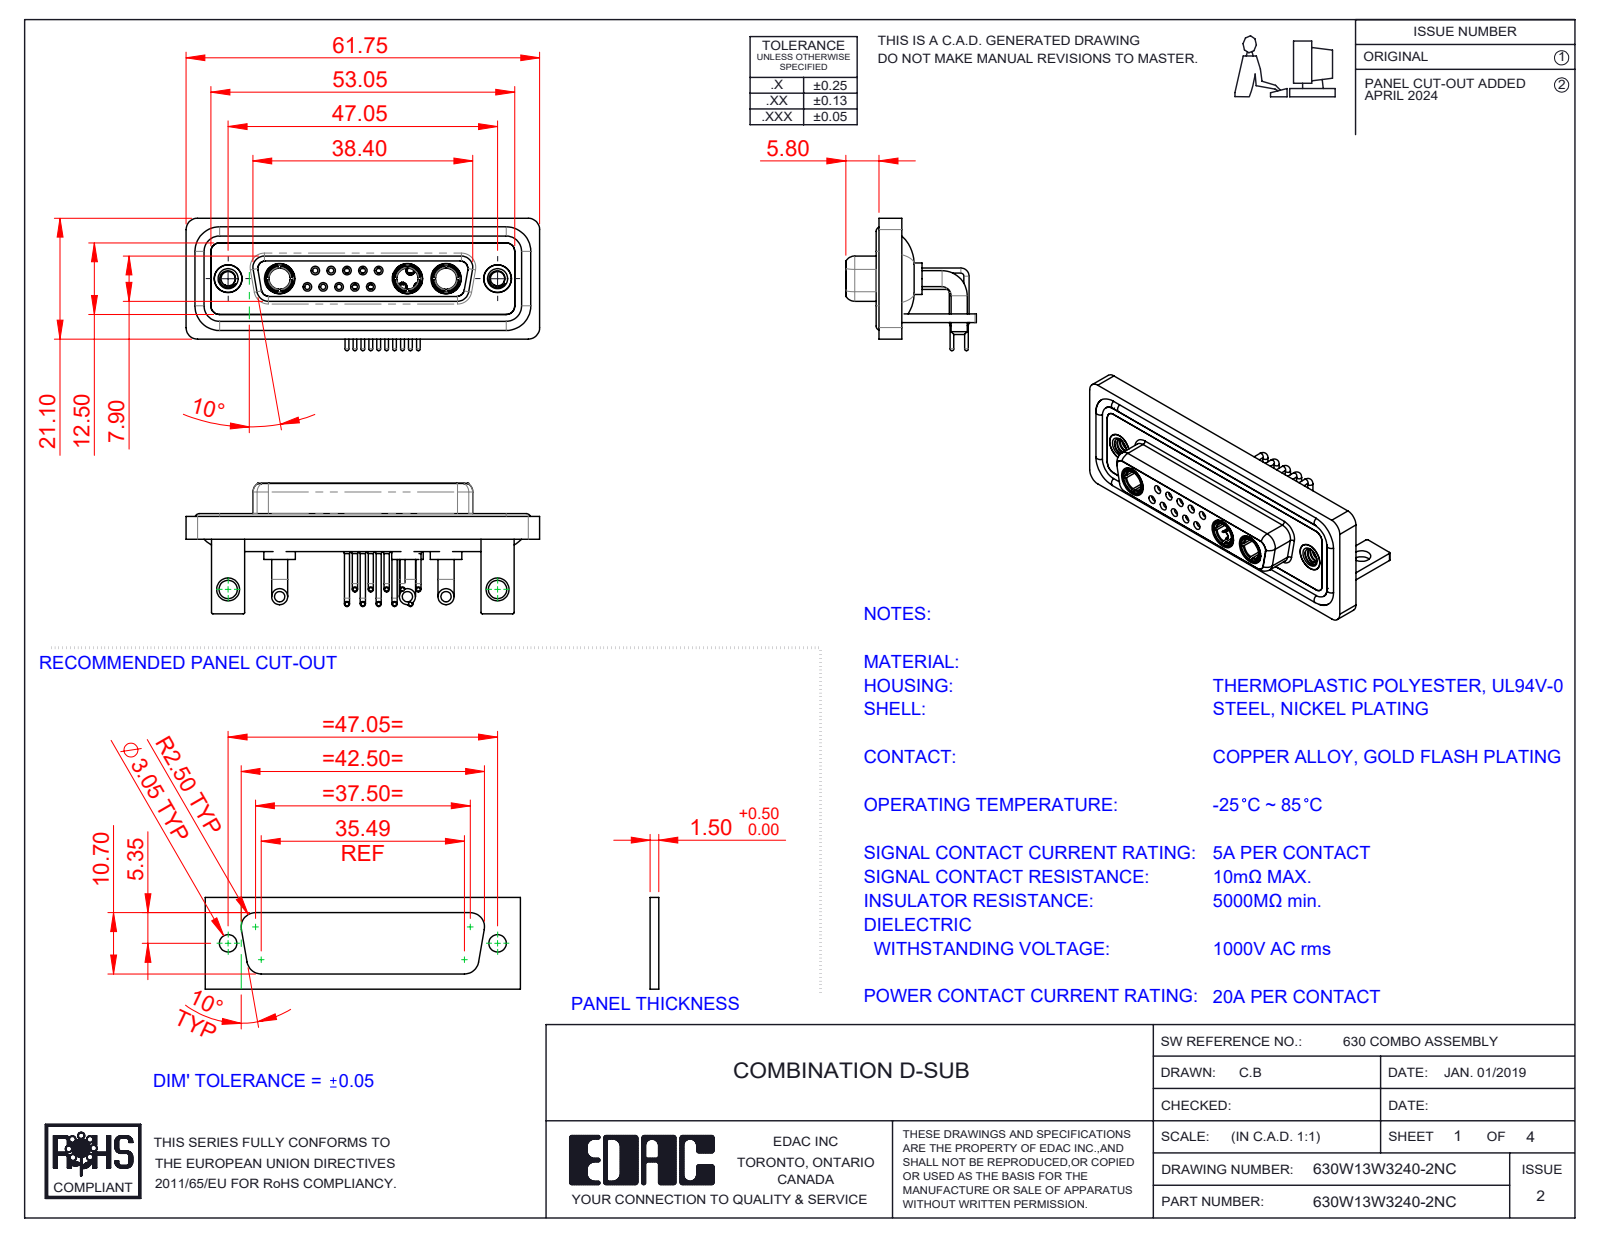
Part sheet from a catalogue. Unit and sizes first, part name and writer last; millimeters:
Units: millimetres
Overall size (bounding box): 61.75 × 23.12 × 22.8
Round holes (diameter × count): ⌀0.9 ×10, ⌀1.1 ×10, ⌀1.5 ×10, ⌀2 ×10, ⌀1.6 ×5, ⌀1.7 ×5, ⌀4.85 ×5, ⌀3.7 ×3, ⌀5.3 ×3, ⌀2.5 ×2, ⌀3.2 ×2, ⌀4 ×2
Round bosses / shafts (diameter × count): ⌀0.9 ×15, ⌀1.6 ×12, ⌀0.65 ×10, ⌀2.8 ×6, ⌀2 ×5, ⌀1.5 ×5, ⌀5.5 ×3, ⌀5.2 ×3
Partial cylindrical surfaces — rounded edges, fillets, slot ends (radius × count): R2 ×19, R1.5 ×18, R0.25 ×16, R1.35 ×8, R1.6 ×8, R0.5 ×5, R0.6 ×4, R0.65 ×4
Main face-to-face distances: 0.4, 1.8, 2.9, 3.7, 1.5, 4.1, 1.1, 1.4, 1.6, 3.1
Hole centre spacings: 3.16, 2.77, 5.54, 5.04, 8.31, 5.03, 7.49, 11.08
Volume: 8 830 mm³ · Surface area: 15 035 mm²
Bodies: 25 solids, 1192 faces (362 planar, 515 cylindrical, 315 other)
Part name (STEP PRODUCT): 630Combo Housing_13W3; 630Combo Threaded Rivet_A; 630Combo Shell Rear_25 Contacts; 630Combo Waterproof Housing_25 Contacts (+6 more)
STEP written by: SolidWorks 2023 (CONFIG_CONTROL_DESIGN)
